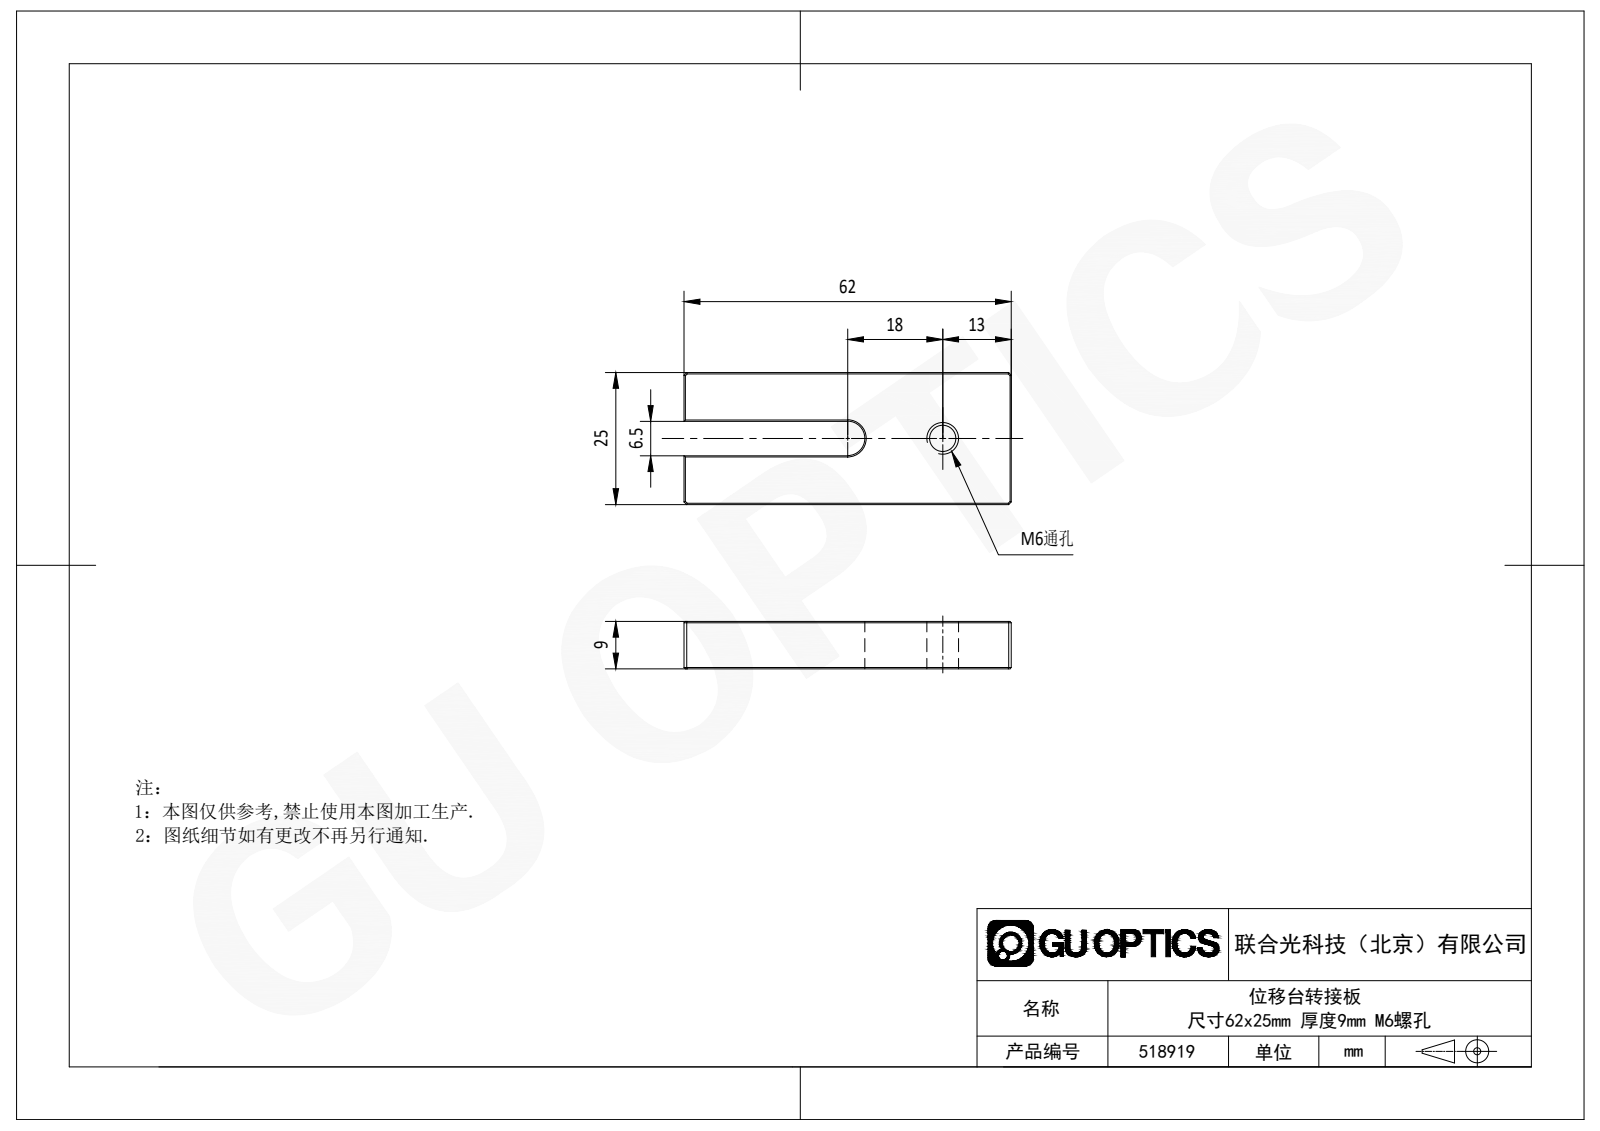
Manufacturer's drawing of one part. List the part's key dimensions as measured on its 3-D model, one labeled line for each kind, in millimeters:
STEP written by: SolidWorks 2020 (CONFIG_CONTROL_DESIGN)
Units: millimetres
Bodies: 1 solid, 40 faces (35 planar, 2 cylindrical, 3 other)
Overall size (bounding box): 62 × 25 × 9
Volume: 11 789 mm³ · Surface area: 4 837 mm²
Round holes (diameter × count): ⌀5 ×1
Partial cylindrical surfaces — rounded edges, fillets, slot ends (radius × count): R3.25 ×1
Main face-to-face distances: 9, 9.25, 15.75, 25, 6.5, 62, 11.13, 12.55, 23.68, 1.42
